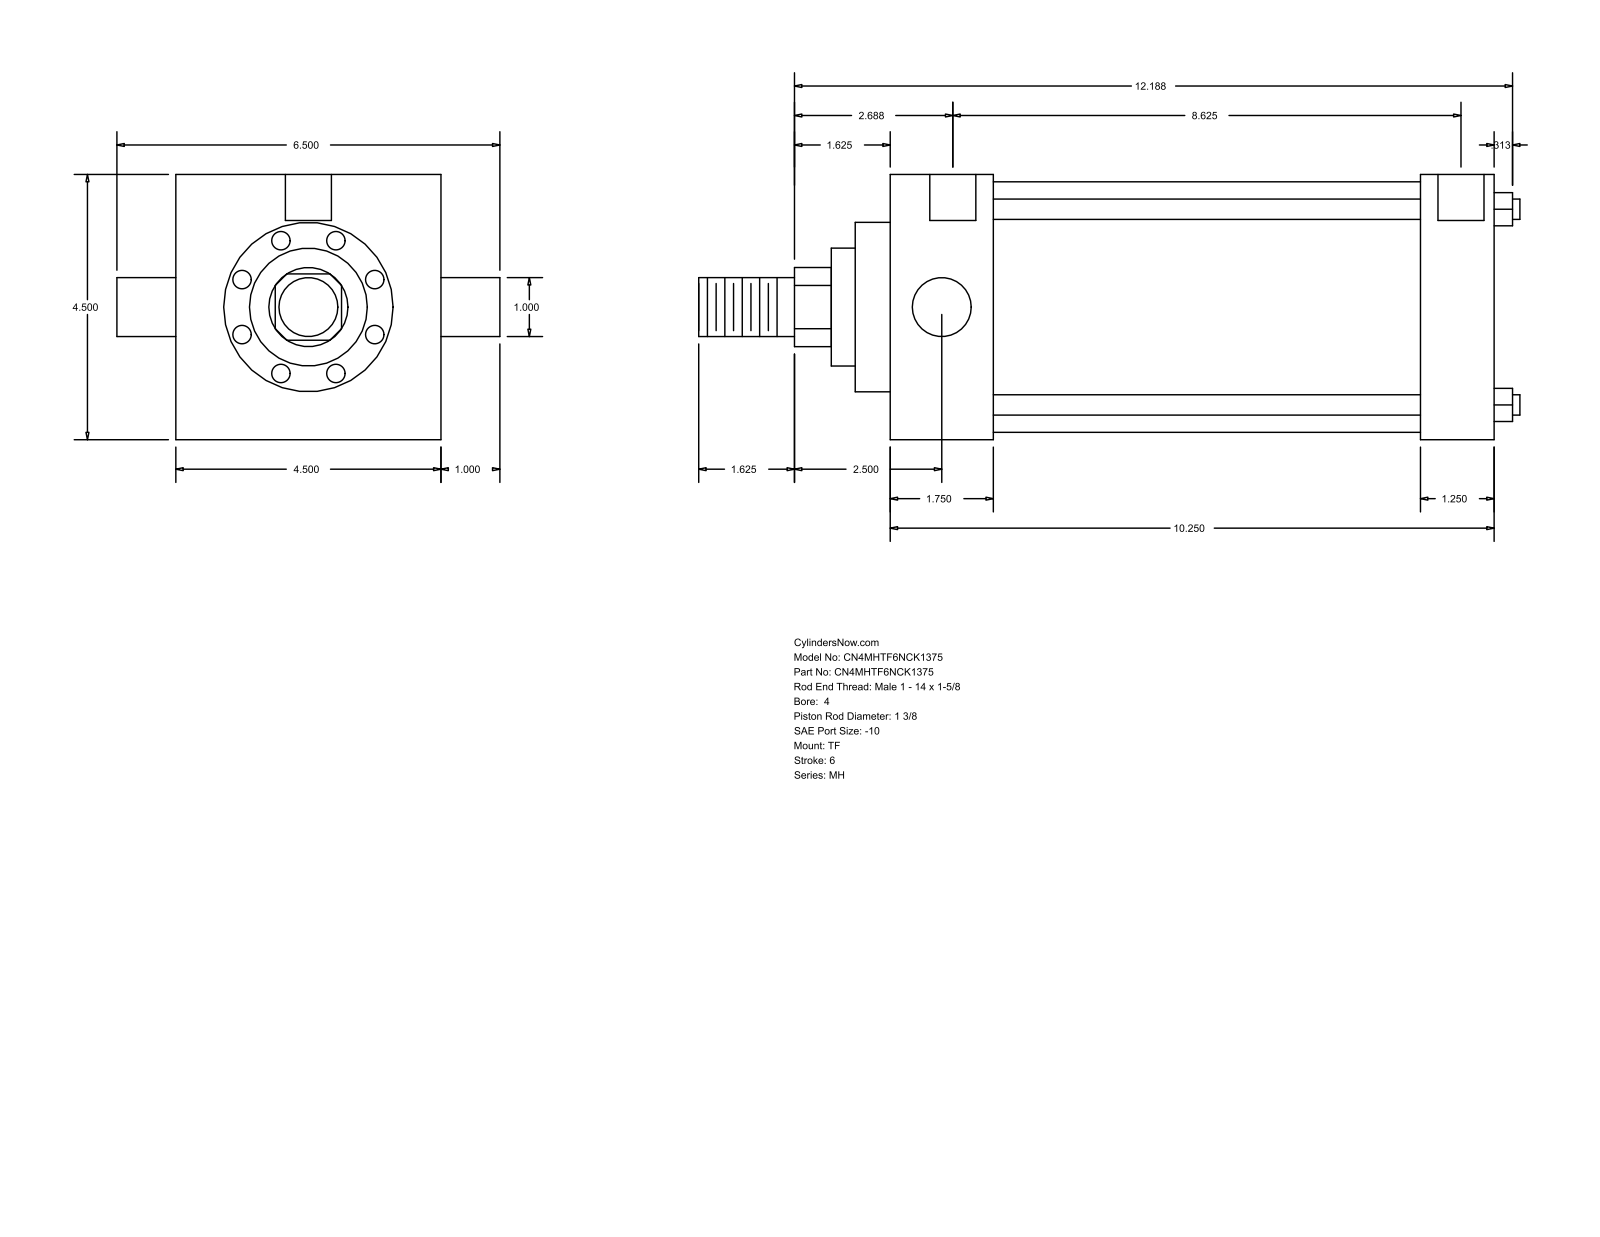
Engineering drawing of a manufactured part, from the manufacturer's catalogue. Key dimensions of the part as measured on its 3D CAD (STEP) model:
Part name (STEP PRODUCT): MH_TF__0400_1.375
STEP written by: GSSL Pune (CONFIG_CONTROL_DESIGN)
Units: millimetres
Bodies: 0 solids, 86 faces (61 planar, 25 cylindrical, 0 other)
Overall size (bounding box): 354.01 × 165.1 × 114.3
Round holes (diameter × count): ⌀8.73 ×3, ⌀19.84 ×2
Round bosses / shafts (diameter × count): ⌀8.76 ×4, ⌀25.4 ×2, ⌀107.95 ×1, ⌀73.03 ×1, ⌀50.8 ×1, ⌀34.92 ×1
Partial cylindrical surfaces — rounded edges, fillets, slot ends (radius × count): R17.06 ×1
Main face-to-face distances: 114.3, 260.35, 44.45, 215.9, 228.61, 184.16, 31.74, 15.08, 59.53, 243.69
Hole centre spacings: 1.59, 220.67, 219.08, 222.26
